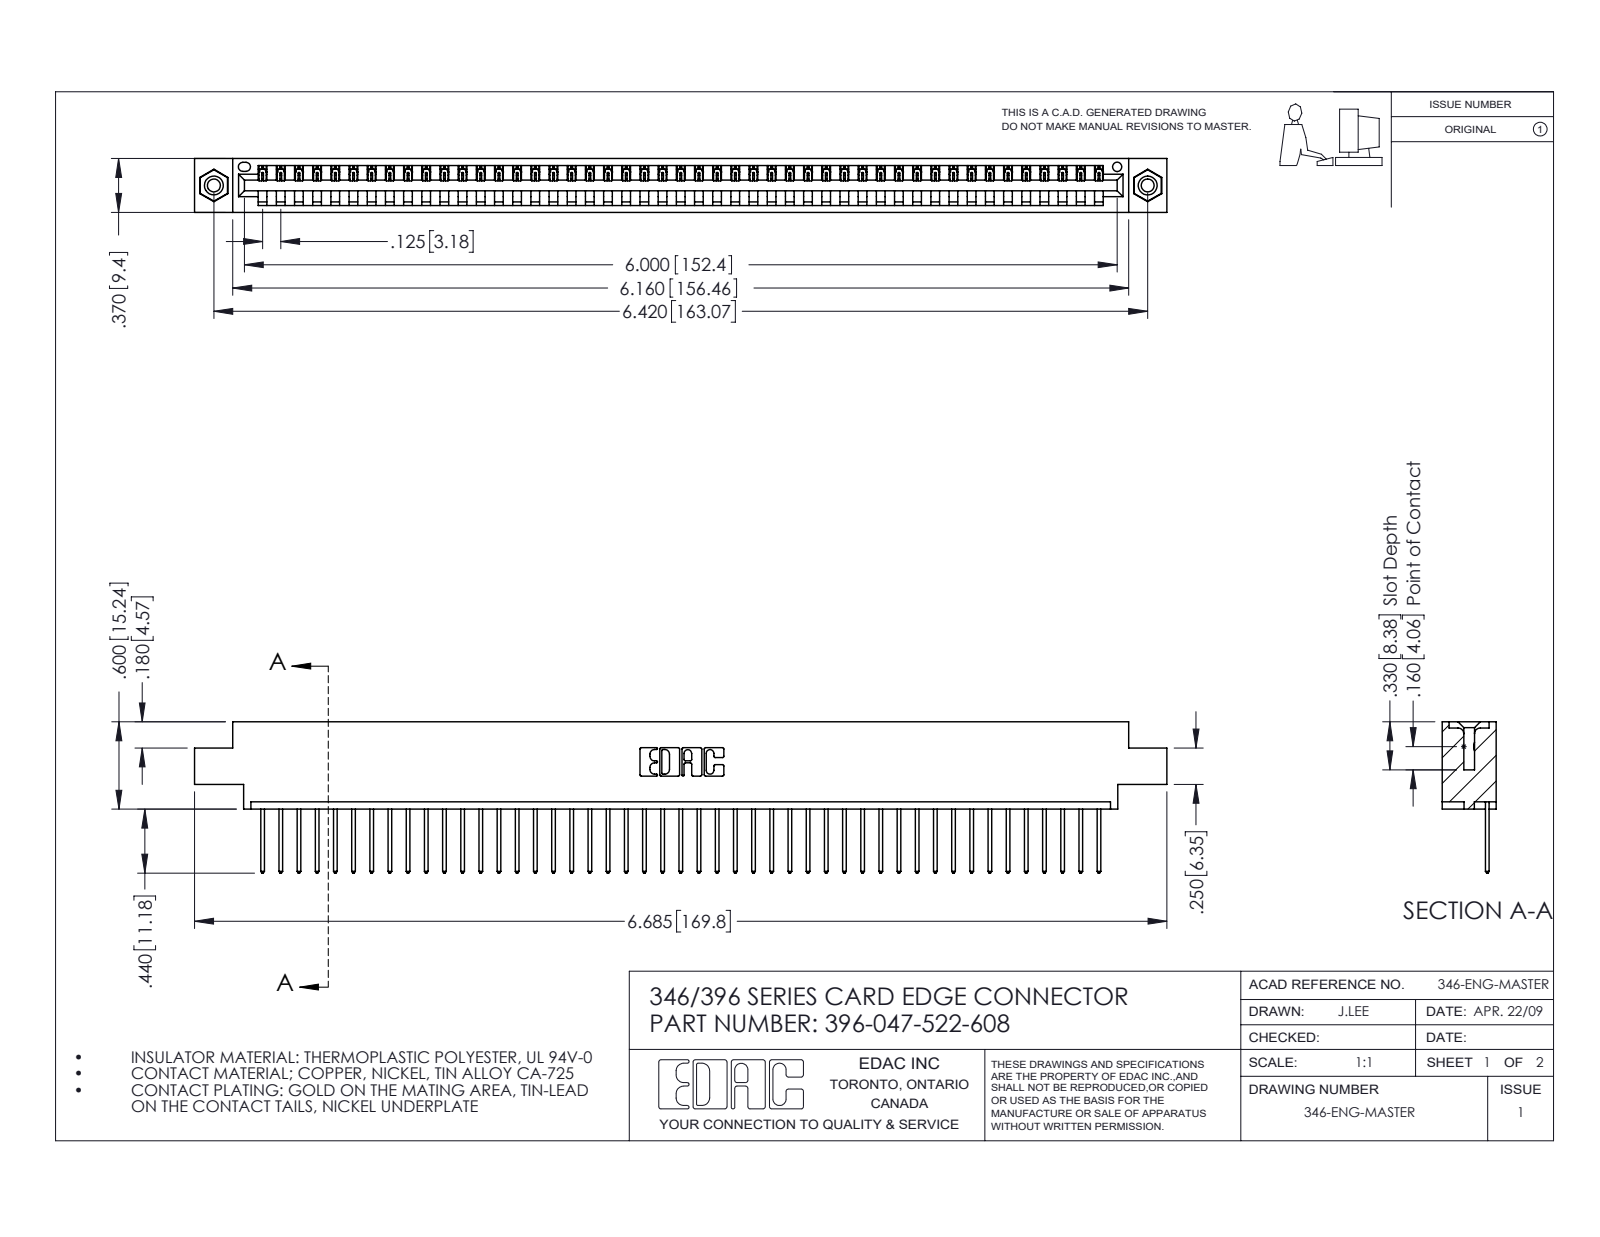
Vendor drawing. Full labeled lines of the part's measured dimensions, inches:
Part name (STEP PRODUCT): 396-047-522-608; 345-250-001_345-250-003-102; 345-292-001_345-293-122; 346 Part_0.170 Offset - 0.156 Dia-TI
STEP written by: SolidWorks 2016 (CONFIG_CONTROL_DESIGN)
Units: inches
Bodies: 50 solids, 2912 faces (1992 planar, 904 cylindrical, 16 other)
Overall size (bounding box): 6.685 × 1.04 × 0.37
Volume: 0.984 in³ · Surface area: 31.89 in²
Round holes (diameter × count): ⌀0.089 ×2, ⌀0.125 ×2, ⌀0.156 ×2, ⌀0.064 ×1
Round bosses / shafts (diameter × count): ⌀0.155 ×2
Partial cylindrical surfaces — rounded edges, fillets, slot ends (radius × count): R0.006 ×94, R0.01 ×94, R0.01 ×22, R0.007 ×6, R0.031 ×6, R0.026 ×3, R0.031 ×2, R0.04 ×2
Main face-to-face distances: 0.048, 0.322, 0.37, 0.25, 0.072, 0.298, 0.025, 0.222, 0.148, 0.1
Hole centre spacings: 0.246, 6.211, 6.42
